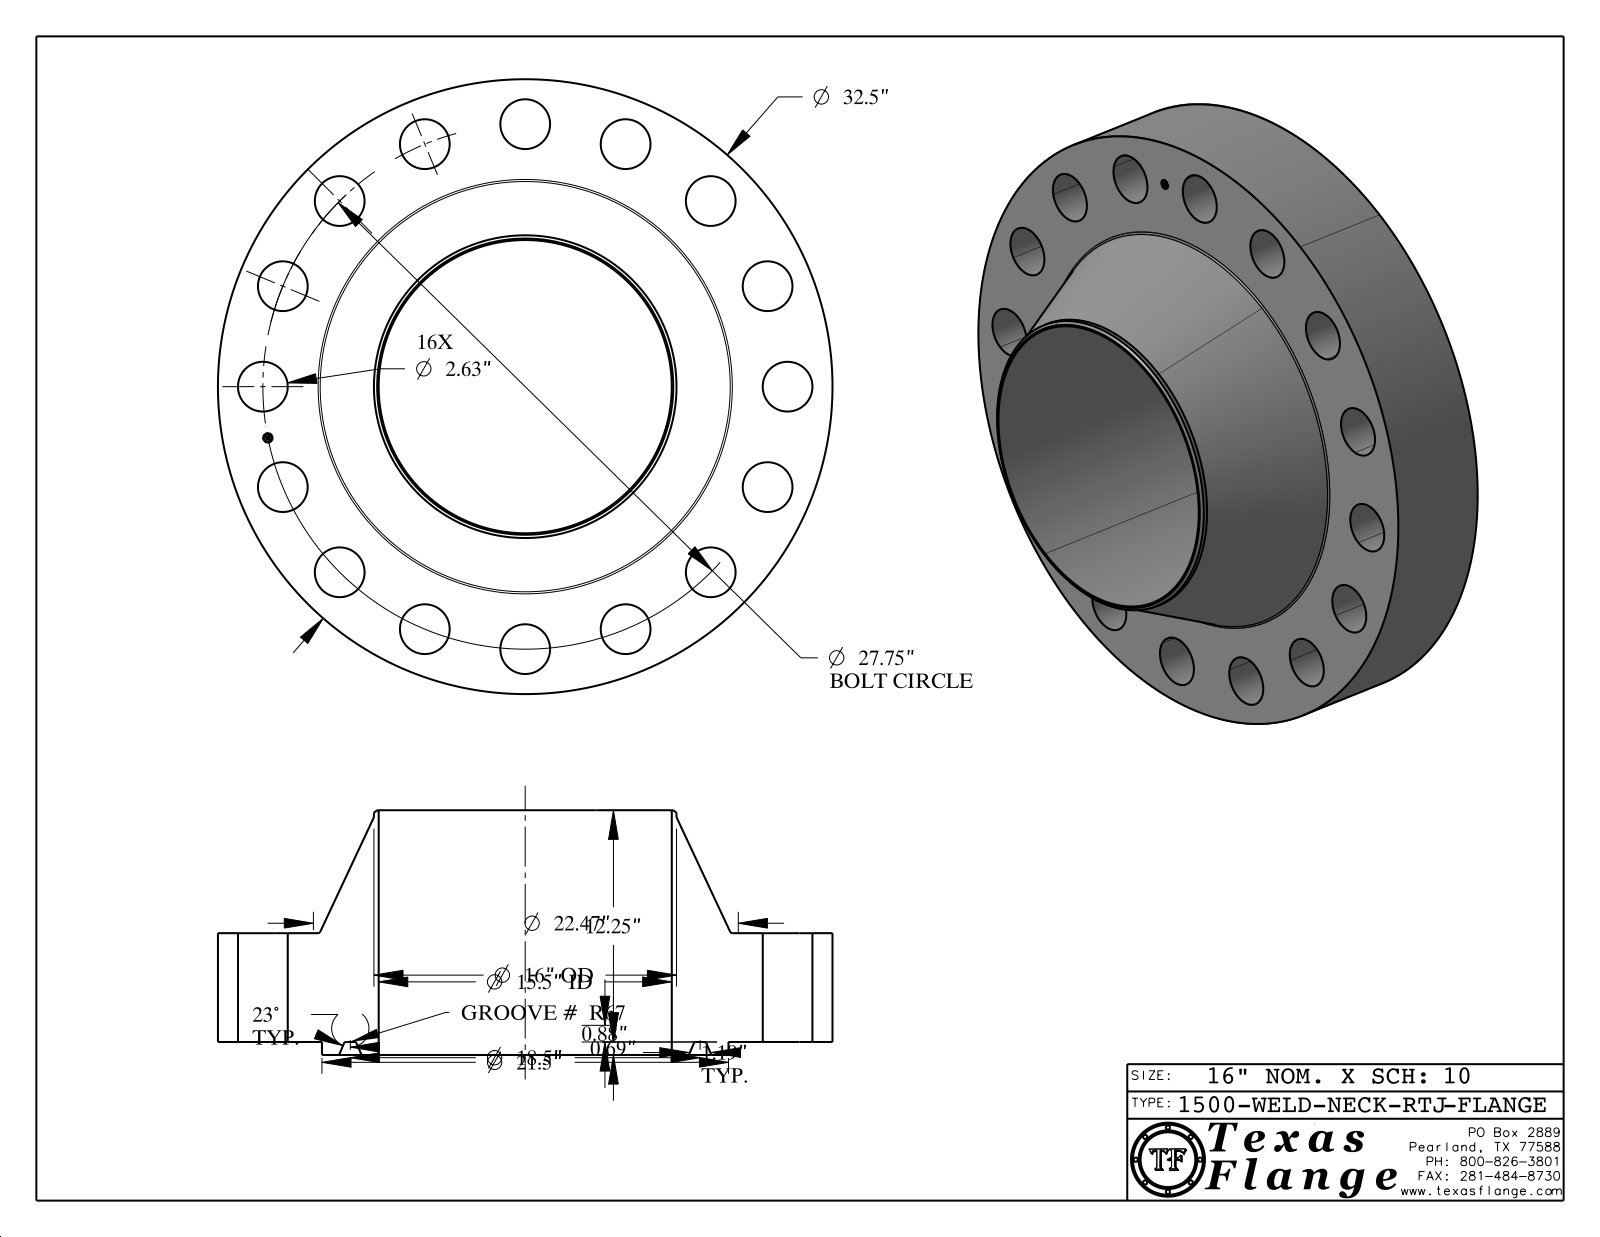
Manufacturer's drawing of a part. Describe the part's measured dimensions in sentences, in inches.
The part is named "1500-WELD-NECK-RTJ". Its 3-D file was written by "CATIA V5 STEP AP214 (AUTOMOTIVE_DESIGN)". It is 1 solid with 445 faces: 371 planar, 60 cylindrical and 14 other. Overall it measures 32.5 by 32.5 by 12.938 inches. Its volume is 3 846 cubic inches and its surface area 3 427 square inches. Round holes: 16 of diameter 2.63, 1 of diameter 0.495, 1 of diameter 15.5. Round bosses or shafts: 8 of diameter 0.03, 1 of diameter 32.5, 1 of diameter 21.5, 1 of diameter 16, 1 of diameter 0.39. The main face-to-face distances are 5.75, 0.688, 6.438, 12.938, 12.25, 6.5, 0.015, 6.423, 5.735, 6.515. The hole center spacings are 5.414, 15.417, 25.638, 27.217, 10.62, 13.875, 19.622, 23.073.
